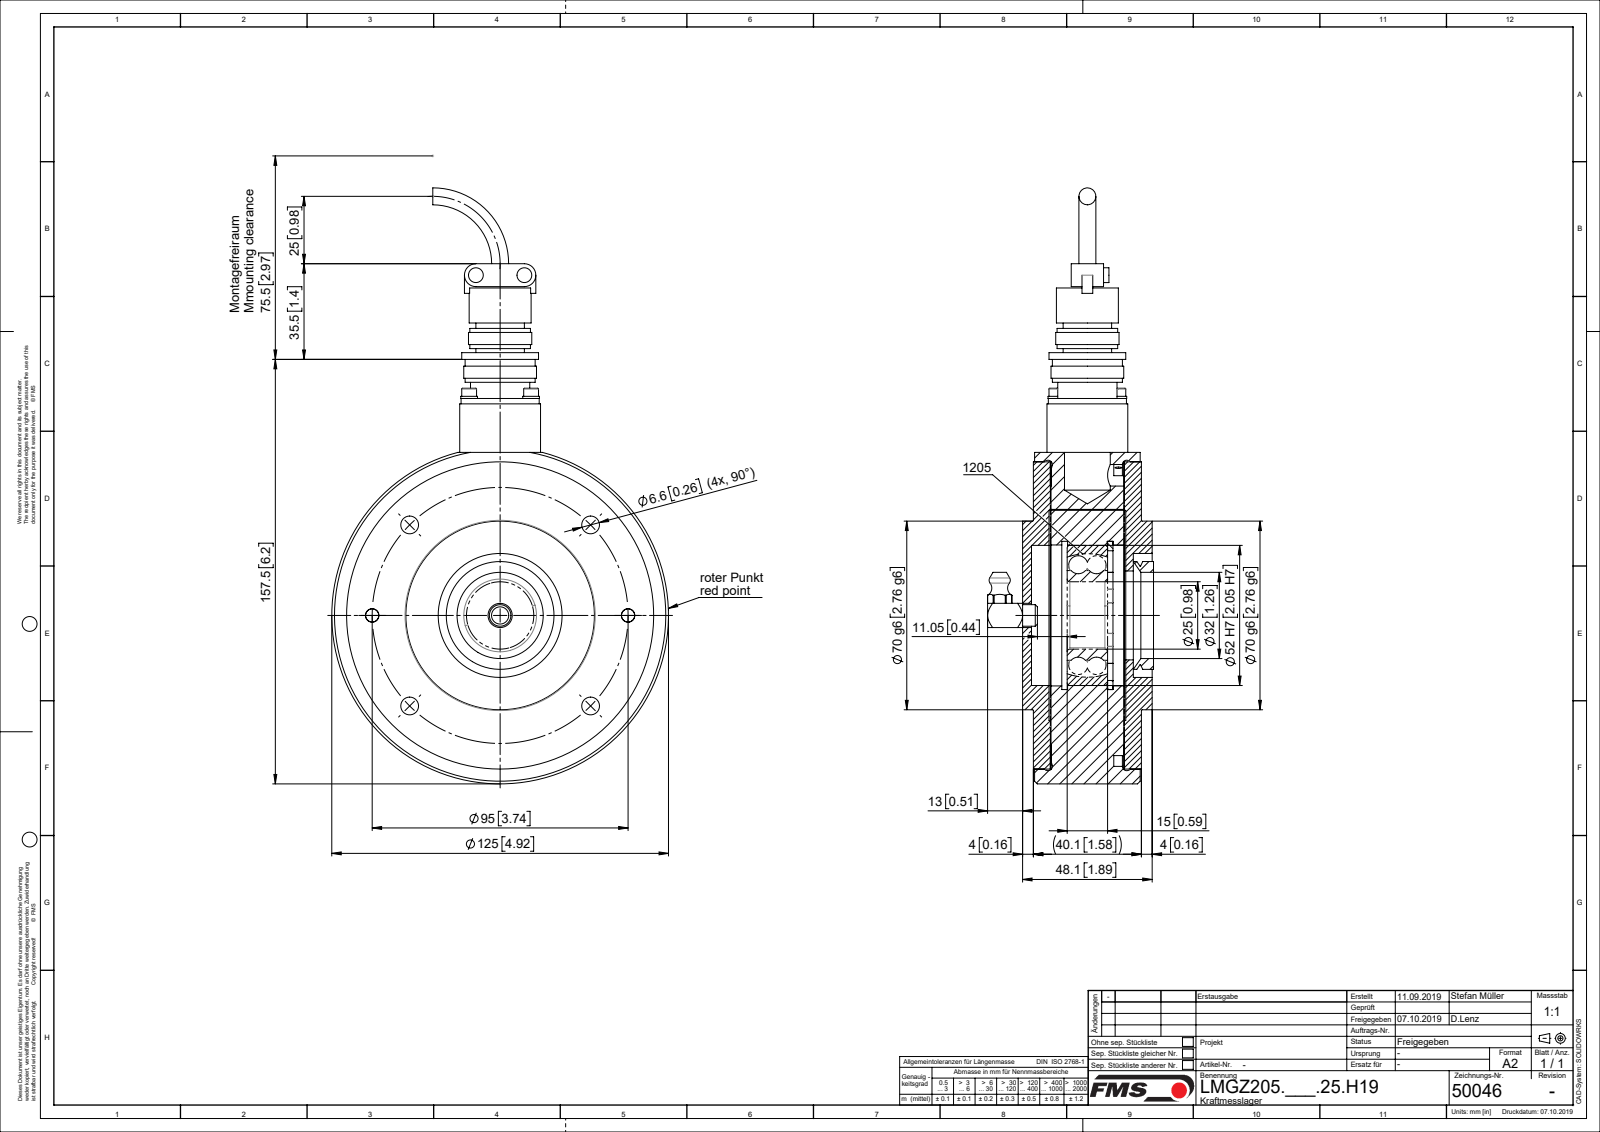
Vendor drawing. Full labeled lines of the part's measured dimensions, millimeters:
Part name (STEP PRODUCT): ZEICHNUNG7; L50046; L4832404; L47955 (+8 more)
STEP written by: Mechanical Desktop 2007 (CONFIG_CONTROL_DESIGN)
Units: millimetres
Bodies: 21 solids, 432 faces (120 planar, 250 cylindrical, 62 other)
Overall size (bounding box): 221.15 × 125 × 62.6
Volume: 482 975 mm³ · Surface area: 145 585 mm²
Round holes (diameter × count): ⌀6.6 ×6, ⌀2.6 ×4, ⌀3.2 ×4, ⌀3.4 ×4, ⌀5 ×2, ⌀11 ×2, ⌀8.68 ×1, ⌀23 ×1, ⌀25 ×1, ⌀31 ×1, ⌀33 ×1, ⌀37.9 ×1
Round bosses / shafts (diameter × count): ⌀5.5 ×6, ⌀6.2 ×4, ⌀3 ×4, ⌀2.5 ×4, ⌀10 ×3, ⌀6 ×2, ⌀125 ×1, ⌀114 ×1
Partial cylindrical surfaces — rounded edges, fillets, slot ends (radius × count): R5 ×8, R4.25 ×2, R40.5 ×1, R47 ×1
Main face-to-face distances: 27.25, 33.55, 6.3, 6.55, 33.8, 27, 27.5, 4, 10.55, 37.8
Hole centre spacings: 47.5, 16.26, 23, 36.36, 67.18, 87.77, 32.53, 95.01
